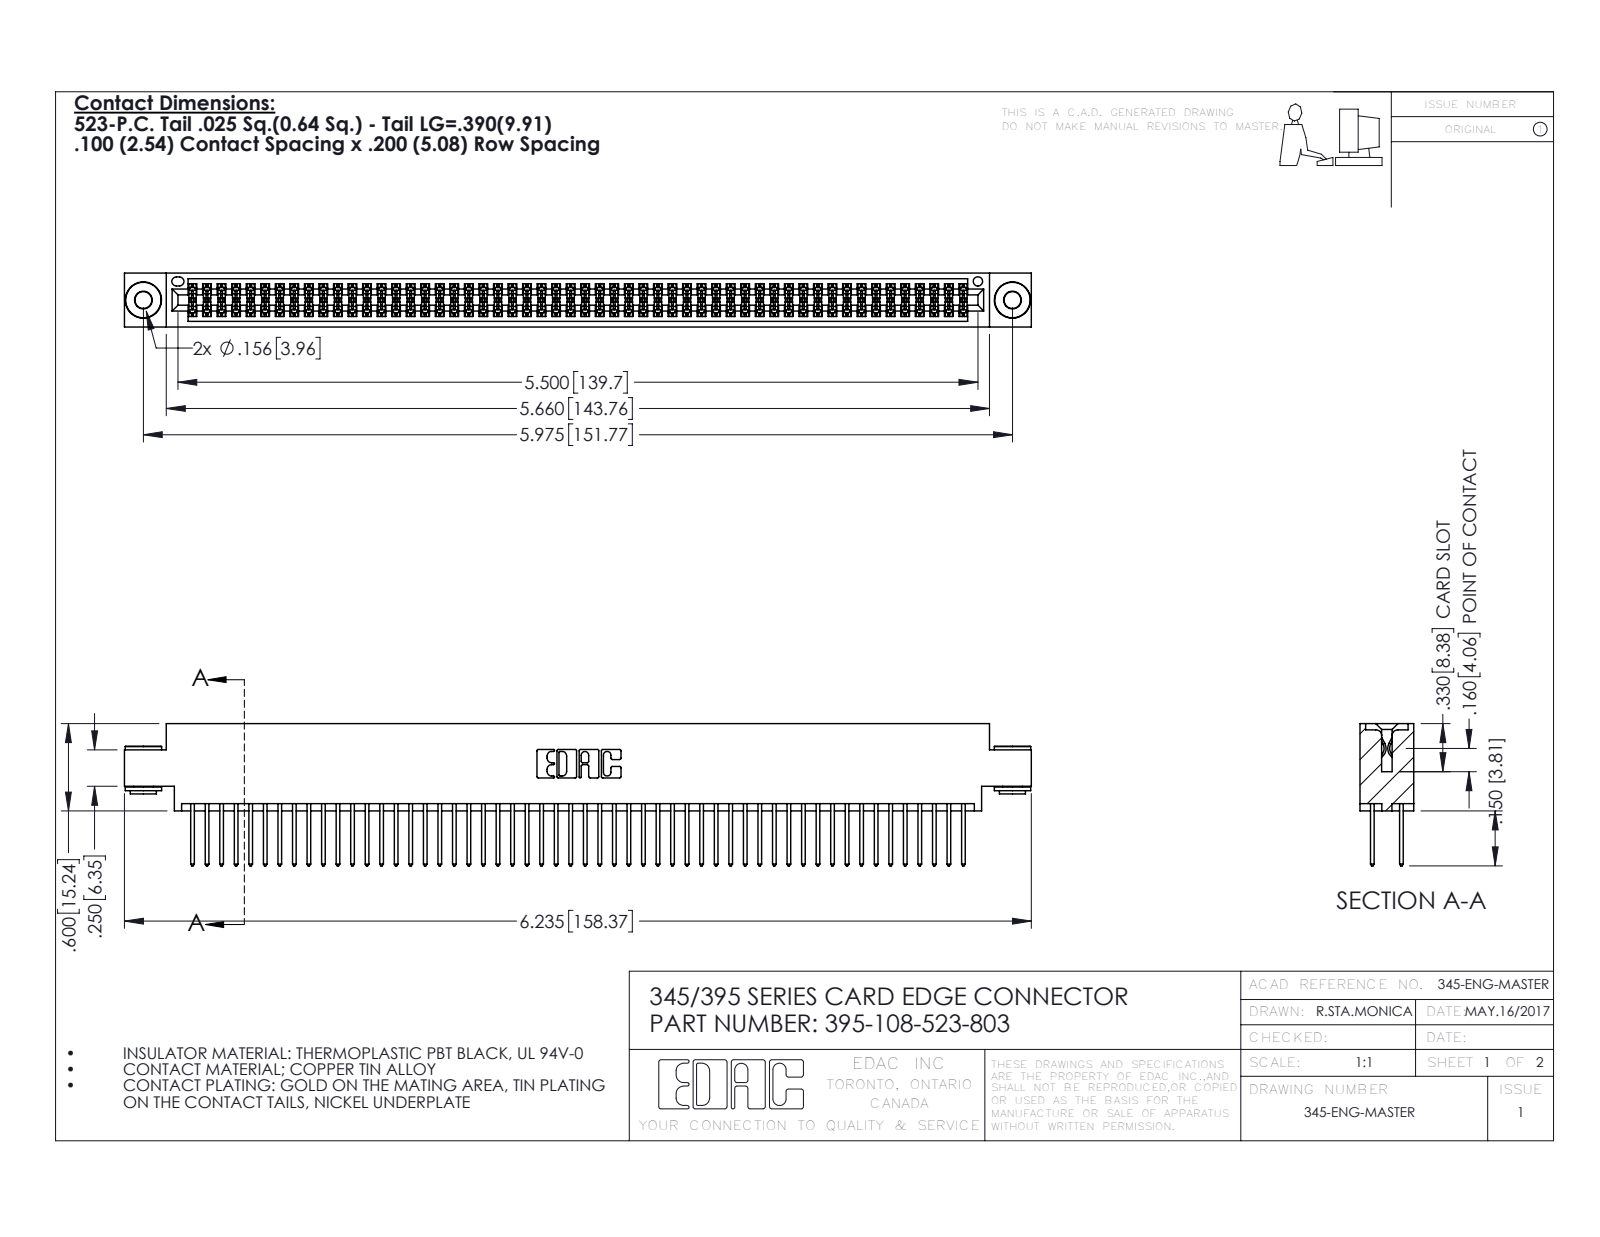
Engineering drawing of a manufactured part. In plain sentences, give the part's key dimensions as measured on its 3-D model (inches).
The part is named "345-250-002_345-250-002-102; 345 Part_0.170 Offset - 0.156 Dia-TH; 395-108-523-803; 345-292-001_345-293-123". Its 3-D file was written by "SolidWorks 2016 (CONFIG_CONTROL_DESIGN)". It is 111 solids with 5568 faces: 3658 planar, 1902 cylindrical and 8 other. Overall it measures 6.235 by 0.977 by 0.37 inches. Its volume is 0.953 cubic inches and its surface area 38.23 square inches. Round holes: 2 of diameter 0.116, 2 of diameter 0.156, 1 of diameter 0.064. Round bosses or shafts: 2 of diameter 0.25, 2 of diameter 0.18, 2 of diameter 0.136. Partial cylindrical surfaces (rounded edges, fillets, slot ends): 162 of radius 0.006, 108 of radius 0.01, 22 of radius 0.01, 6 of radius 0.007, 6 of radius 0.031, 3 of radius 0.026, 2 of radius 0.014, 2 of radius 0.019. The main face-to-face distances are 0.072, 0.298, 0.2, 0.098, 0.272, 0.025, 0.37, 0.225, 0.175, 0.149. The hole center spacings are 0.27, 5.739, 5.975.
